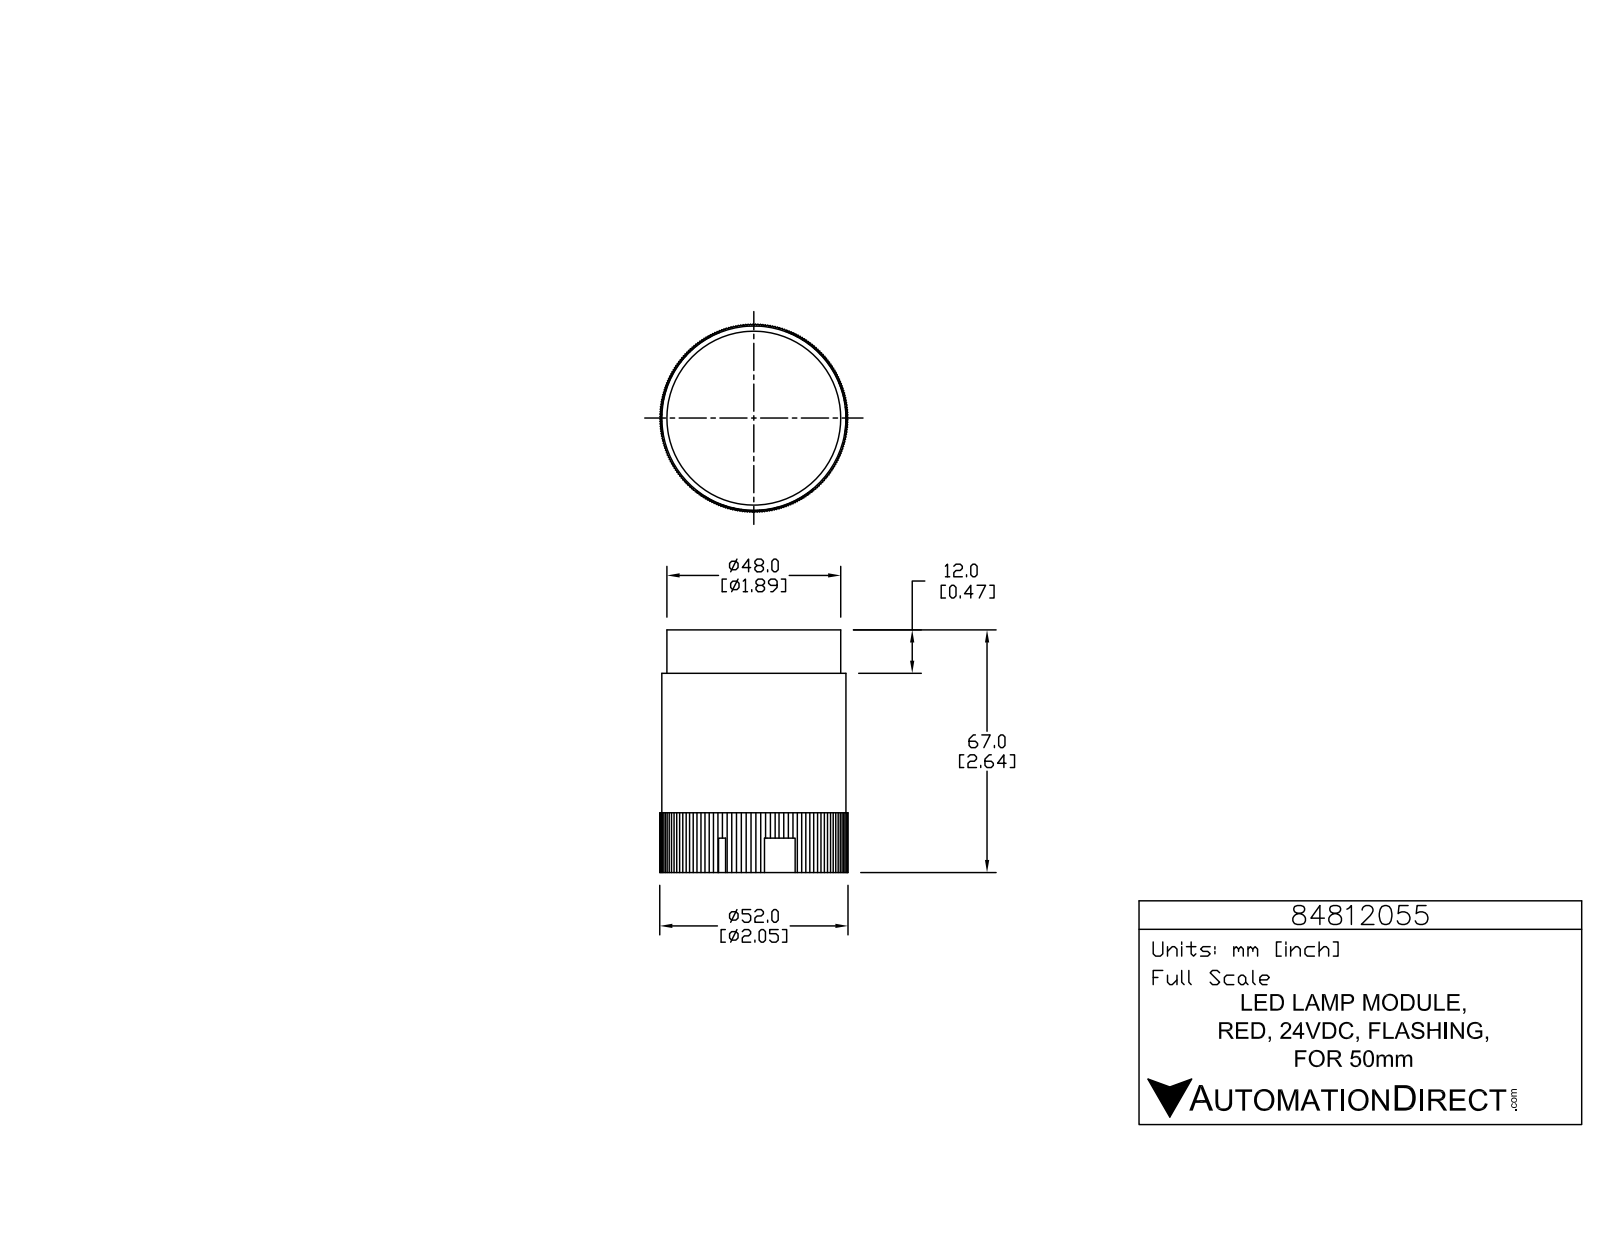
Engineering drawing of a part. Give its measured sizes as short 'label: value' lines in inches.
name: 84812055
written by: SolidWorks 2015 (AUTOMOTIVE_DESIGN)
unit: in
bodies: 1 solid, 1265 faces (1020 planar, 245 cylindrical, 0 other)
size: 2.638 × 2.047 × 2.047
volume: 6.873 in³; area: 27.62 in²
holes: 3× ⌀0.039, 1× ⌀1.898
bosses: 3× ⌀0.226, 3× ⌀0.056, 1× ⌀2.002, 1× ⌀1.89
rounds: 6× R0.008, 6× R0.008, 6× R0.008, 6× R0.131, 3× R0.004, 3× R0.005, 3× R0.008, 3× R0.008
face distances: 2.165, 1.428, 1.429, 1.429, 0.472, 2.638, 1.428, 1.428, 1.693, 1.988
